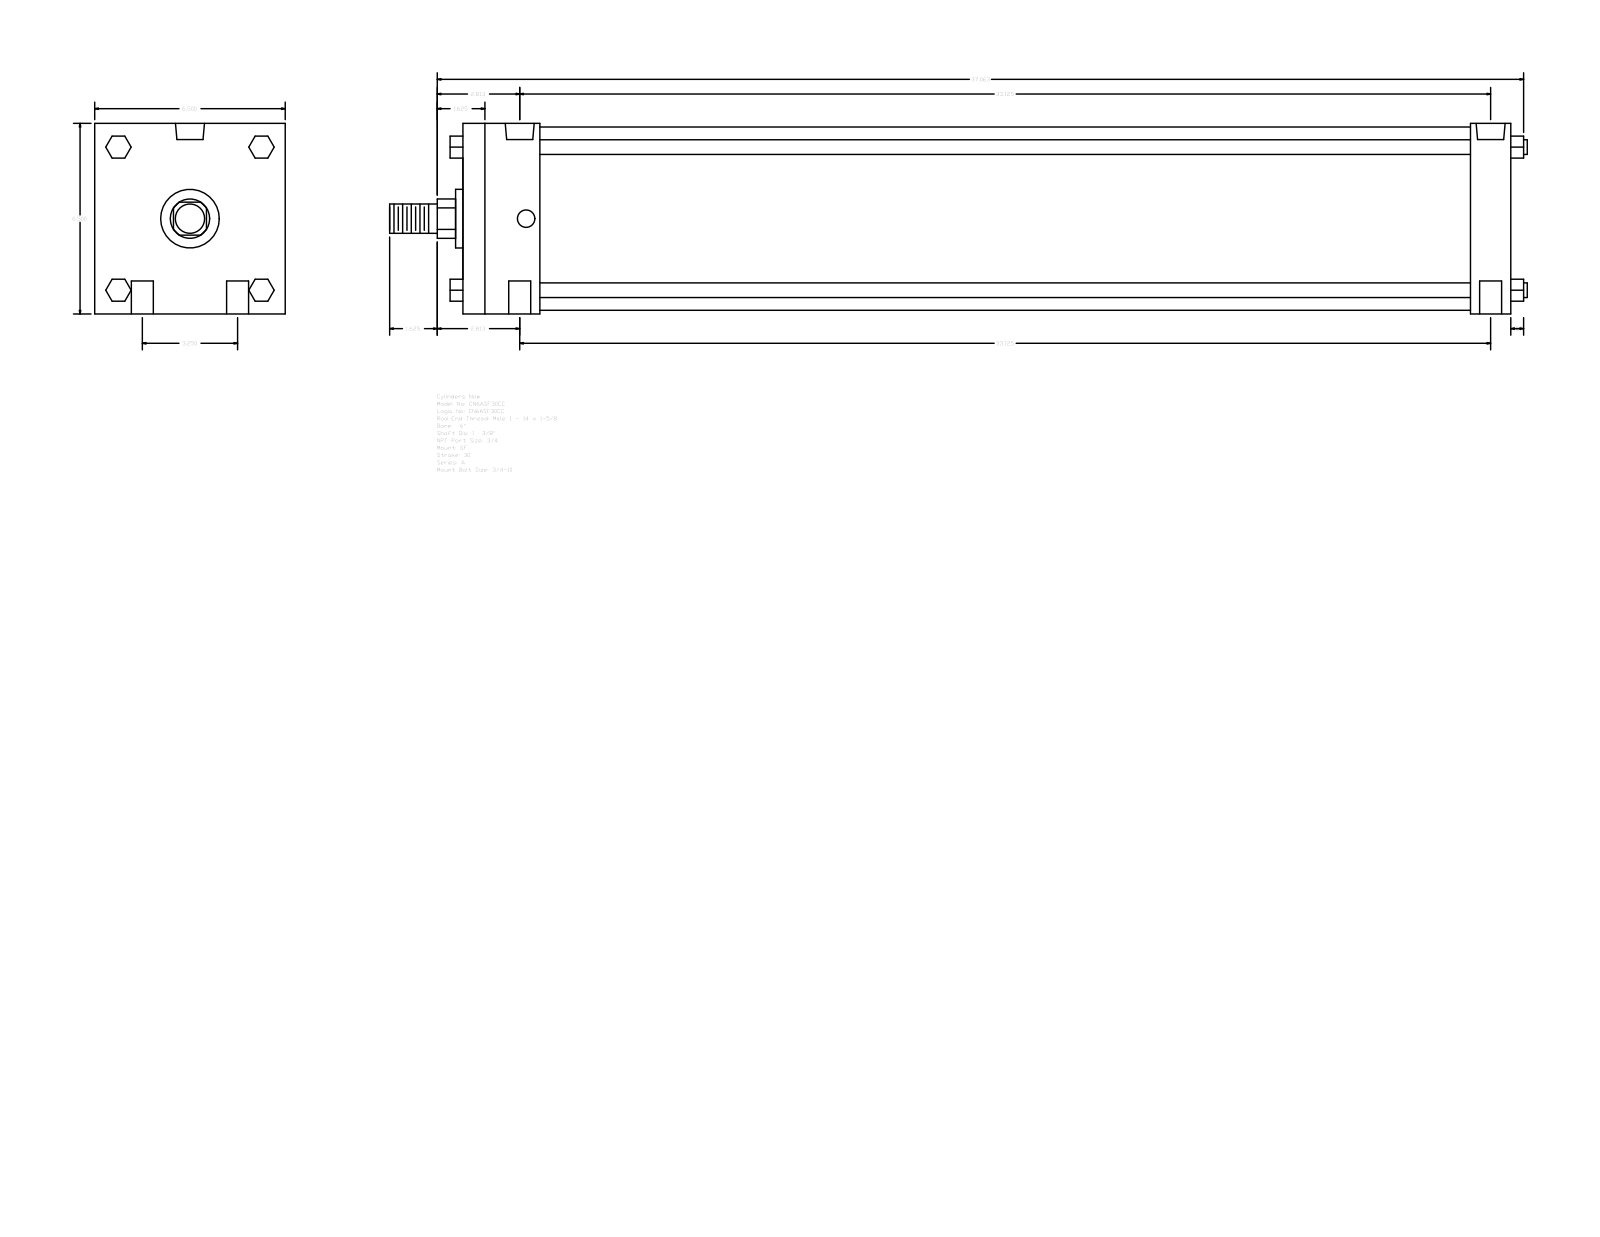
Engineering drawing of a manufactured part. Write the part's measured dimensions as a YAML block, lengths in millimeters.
part_name: "A_SF__0600_1.375"
step_written_by: "GSSL Pune (CONFIG_CONTROL_DESIGN)"
units: millimeters
bodies: {solids: 0, faces: 124, planar: 94, cylindrical: 30, other: 0}
overall_size: [985.84, 165.1, 165.1]
round_holes:
  - {diameter: 19.05, count: 4}
  - {diameter: 15.08, count: 2}
  - {diameter: 25.12, count: 2}
round_bosses_or_shafts:
  - {diameter: 12.7, count: 4}
  - {diameter: 158.75, count: 1}
  - {diameter: 50.8, count: 1}
  - {diameter: 34.92, count: 1}
  - {diameter: 25.4, count: 1}
partial_cylinders:
  - {radius: 17.06, count: 1}
face_to_face_distances: [165.1, 908.04, 873.12, 34.92, 66.67, 806.45, 841.37, 19.05, 61.97, 107.34]
hole_center_spacings: [41.27, 842.38, 841.37, 82.54, 845.41, 830.25]
